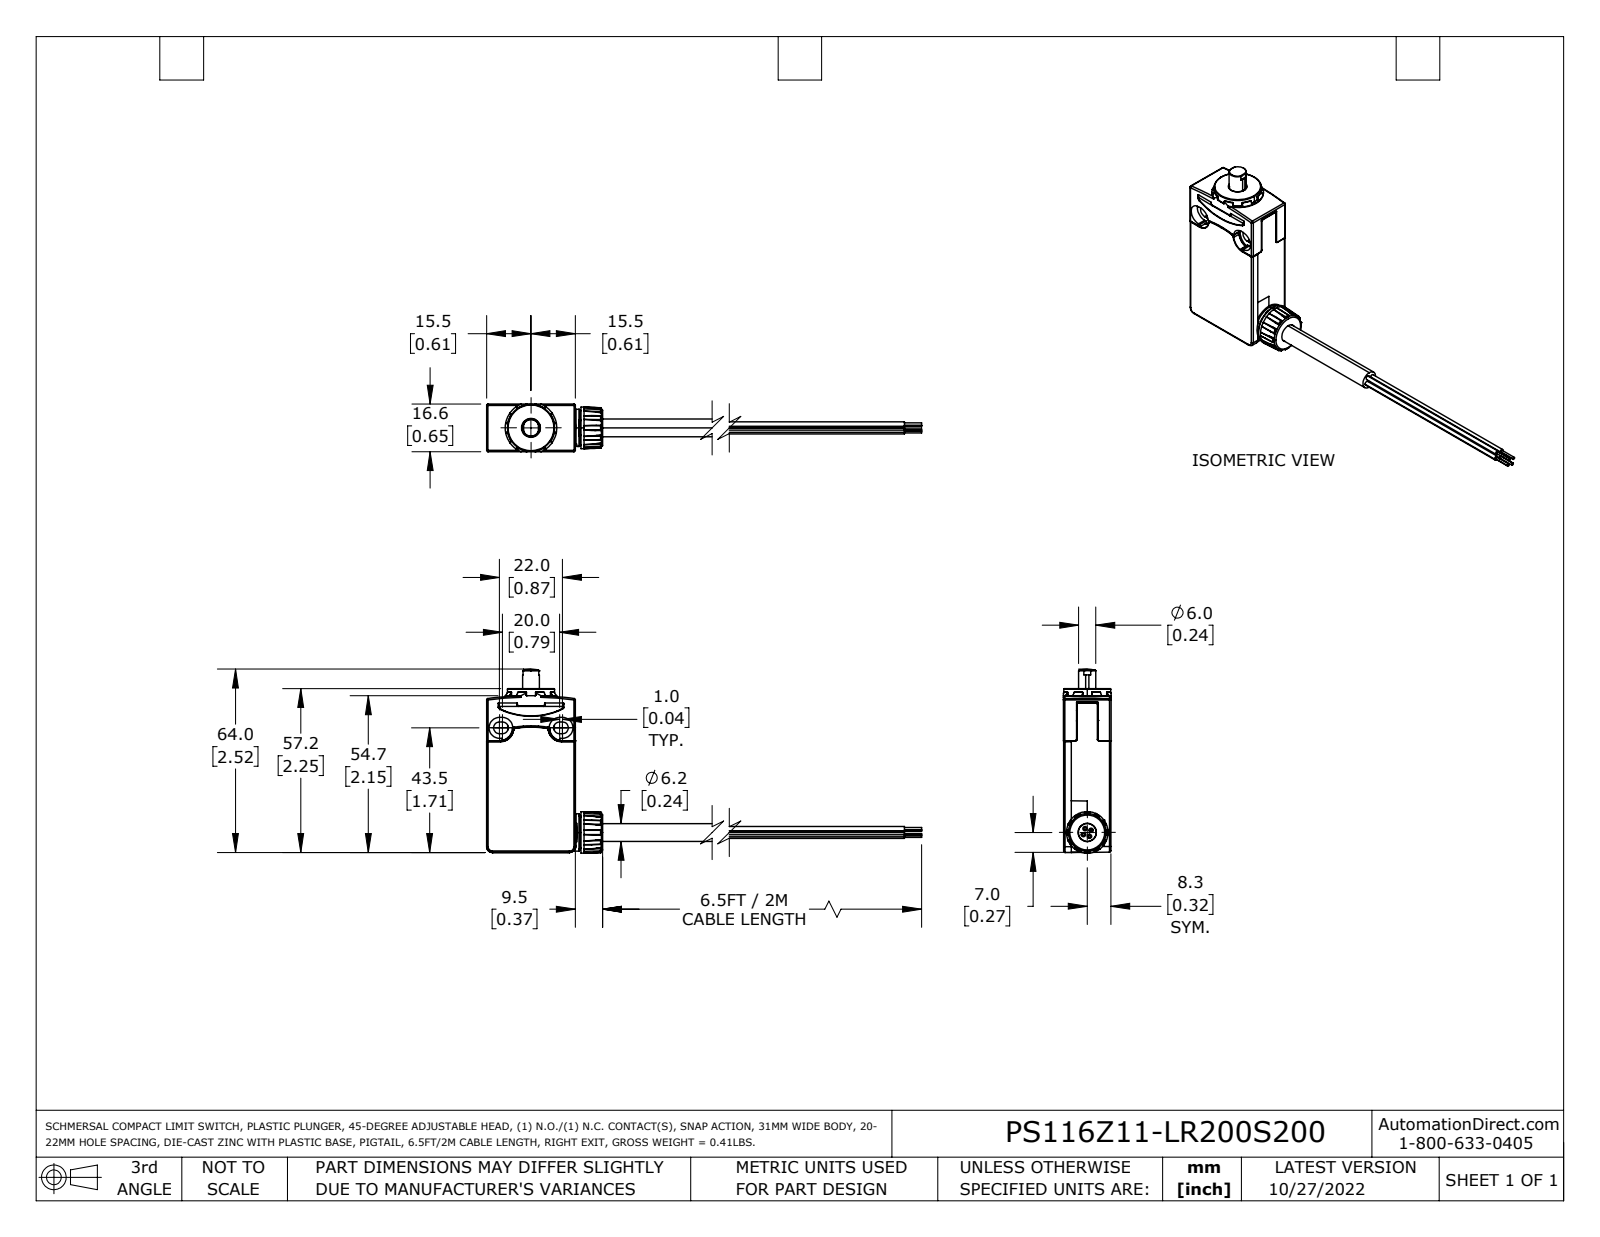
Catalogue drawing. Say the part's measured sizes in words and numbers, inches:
The part is named "PS116Z11-LR200S200_Default". Its 3-D file was written by "SolidWorks 2021 (CONFIG_CONTROL_DESIGN)". It is 1 solid with 1000 faces: 313 planar, 408 cylindrical and 279 other. Overall it measures 5.925 by 2.53 by 0.654 inches. Its volume is 1.835 cubic inches and its surface area 19.44 square inches. Round holes: 2 of diameter 0.079, 1 of diameter 0.244, 1 of diameter 0.252, 1 of diameter 0.48, 1 of diameter 0.571. Round bosses or shafts: 4 of diameter 0.059, 4 of diameter 0.031, 2 of diameter 0.512, 1 of diameter 0.646, 1 of diameter 0.571, 1 of diameter 0.567, 1 of diameter 0.524, 1 of diameter 0.244. Partial cylindrical surfaces (rounded edges, fillets, slot ends): 134 of radius 0.008, 61 of radius 0.004, 30 of radius 0.02, 10 of radius 0.014, 8 of radius 0.039, 6 of radius 0.012, 5 of radius 0.079, 4 of radius 0.081. The main face-to-face distances are 0.65, 0.652, 1.22, 0.118, 0.654, 0.197, 0.177, 0.356, 0.535, 0.116. The hole center spacings are 1.615.
